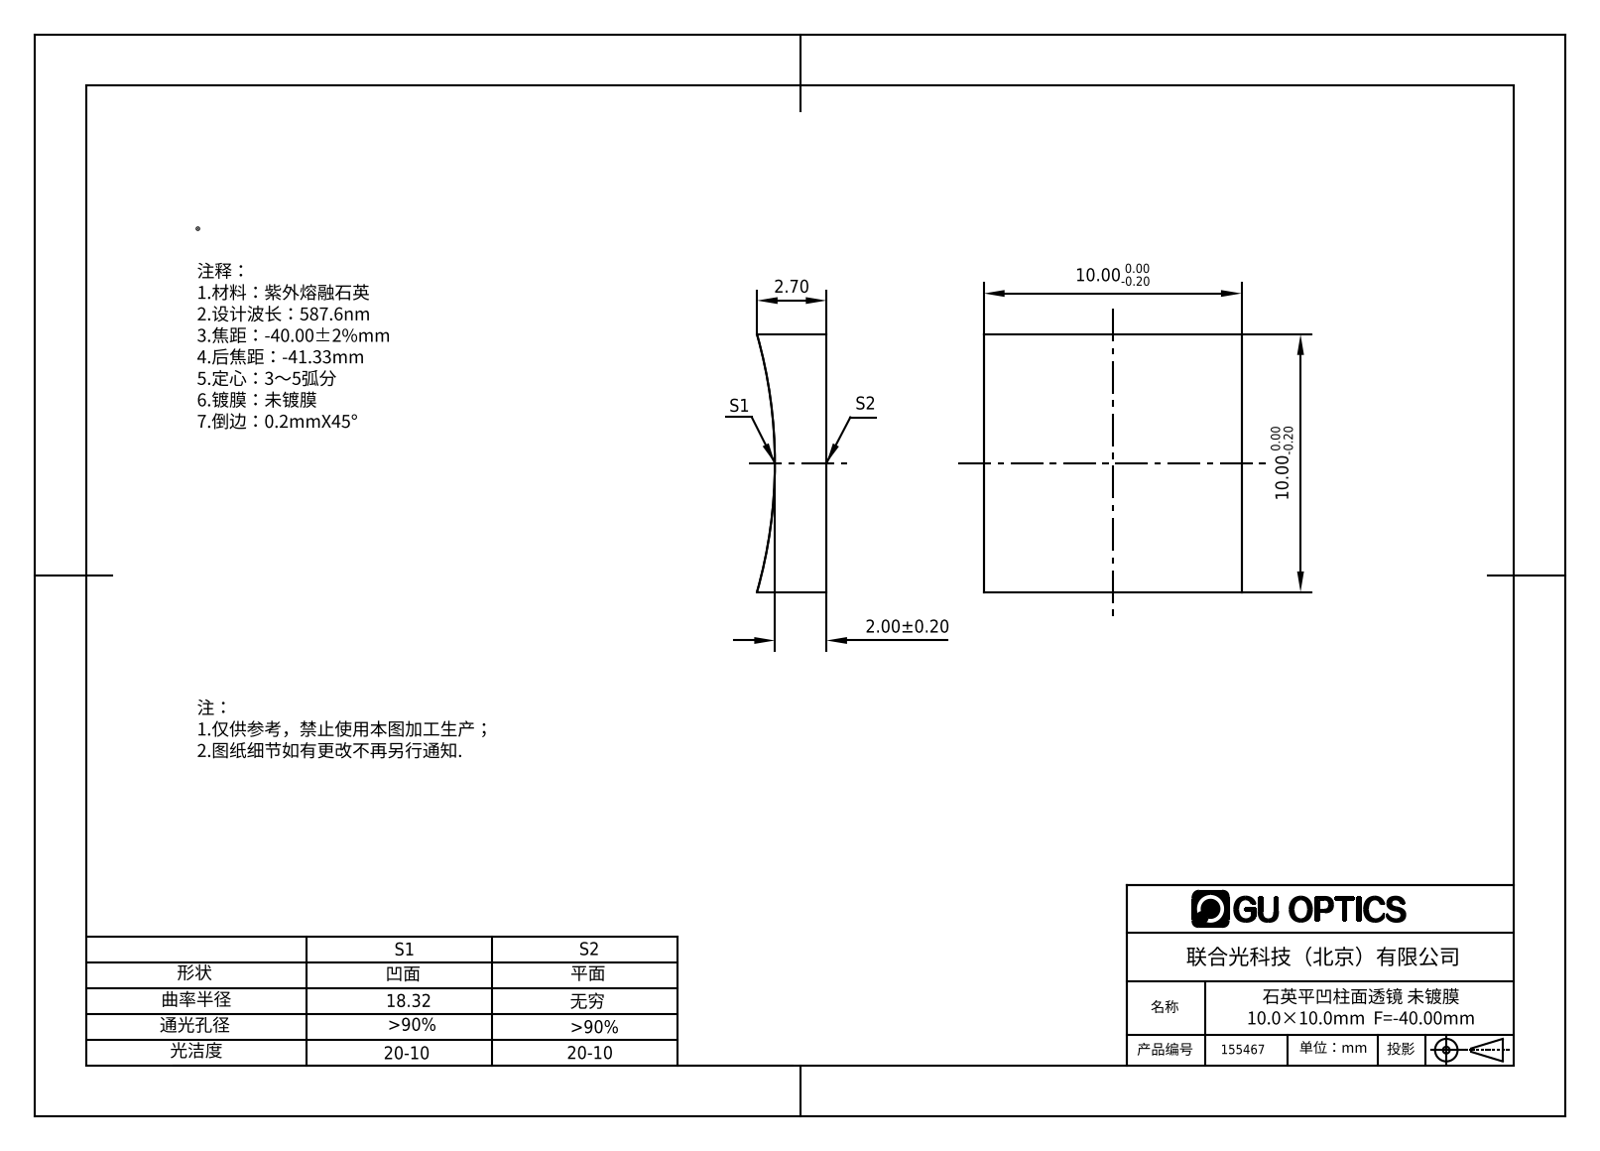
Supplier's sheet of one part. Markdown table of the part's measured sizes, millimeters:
| quantity | value |
| --- | --- |
| part name | 155467 |
| STEP written by | SolidWorks 2016 (AUTOMOTIVE_DESIGN) |
| units | millimeters |
| bodies | 1 solid, 6 faces (5 planar, 1 cylindrical, 0 other) |
| overall size | 10 × 10 × 2.7 |
| volume | 223 mm³ |
| surface area | 300 mm² |
| partial cylindrical surfaces (radius × count) | 18.32 × 1 |
| main face-to-face distances | 10 |
